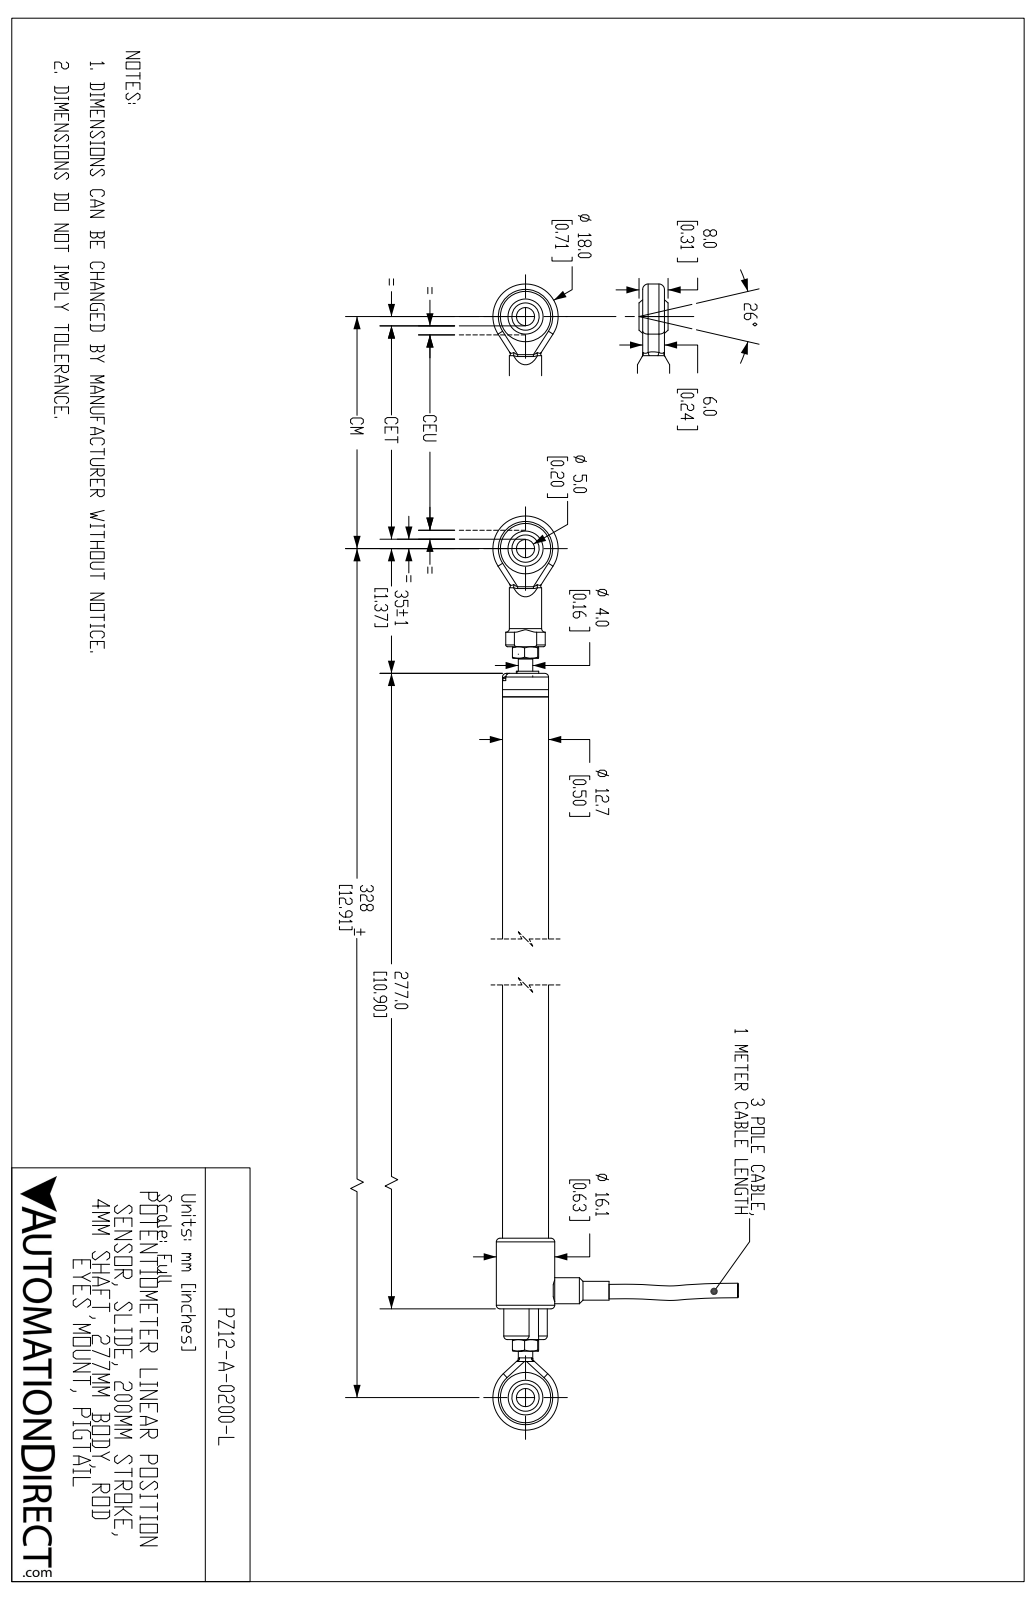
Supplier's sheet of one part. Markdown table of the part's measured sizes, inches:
| quantity | value |
| --- | --- |
| part name | PZ12-A-0200-L |
| STEP written by | SolidWorks 2019 (AUTOMOTIVE_DESIGN) |
| units | inches |
| bodies | 18 solids, 648 faces (168 planar, 170 cylindrical, 310 other) |
| overall size | 13.601 × 2.671 × 0.634 |
| volume | 2.774 in³ |
| surface area | 37.15 in² |
| round holes (diameter × count) | 0.138 × 3, 0.039 × 2, 0.055 × 2, 0.079 × 2, 0.197 × 2, 0.547 × 2, 0.126 × 1, 0.13 × 1, 0.201 × 1, 0.508 × 1 |
| round bosses / shafts (diameter × count) | 0.126 × 4, 0.063 × 4, 0.634 × 1, 0.5 × 1, 0.472 × 1, 0.35 × 1, 0.283 × 1, 0.236 × 1 |
| partial cylindrical surfaces (radius × count) | 0.059 × 8, 0.01 × 4, 0.02 × 2, 0.039 × 2, 0.069 × 2, 0.354 × 2, 0.017 × 1, 0.103 × 1 |
| main face-to-face distances | 0.079, 9.941, 10.02, 0.276, 0.224, 0.213, 0.236, 0.177, 11.195, 0.039 |
| hole center spacings | 0.189, 0.096, 0.167, 0.189, 0.248, 0.285, 0.339, 0.365 |
